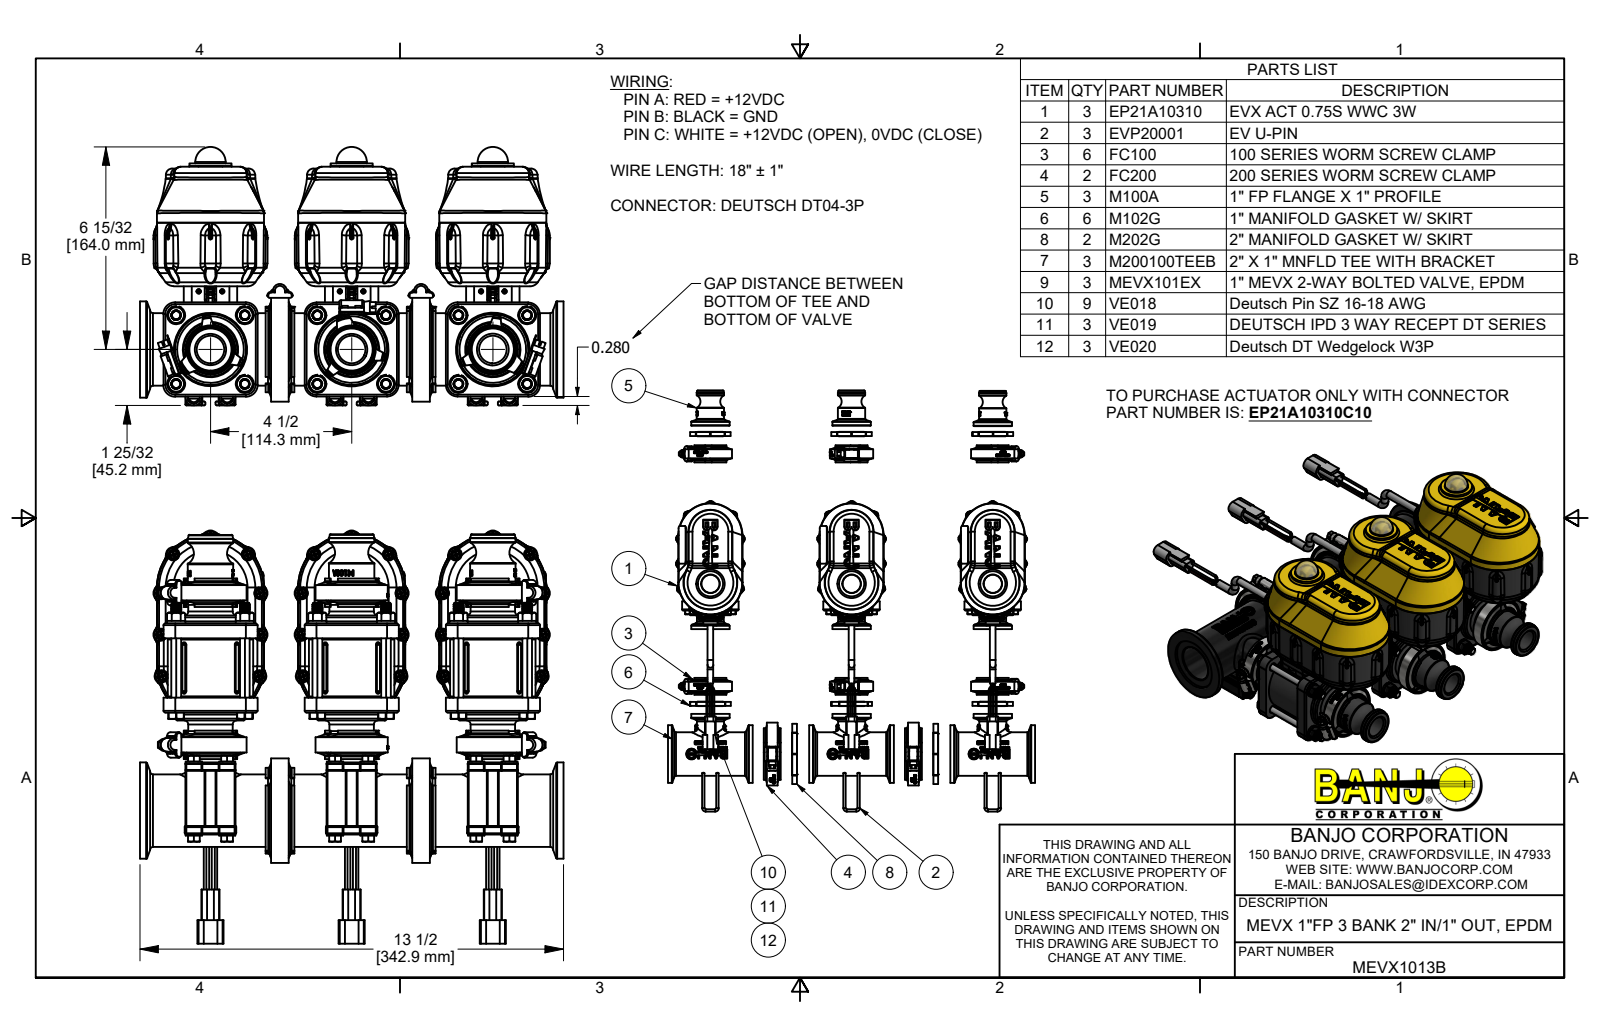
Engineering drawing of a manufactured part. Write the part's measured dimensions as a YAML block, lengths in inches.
part_name: "MEVX1013B; EP21A10310; EP10310; IRF4905 (+8 more)"
step_written_by: "Autodesk Inventor 2021 (AUTOMOTIVE_DESIGN)"
units: inches
bodies: {solids: 340, faces: 42176, planar: 11824, cylindrical: 12081, other: 18271}
overall_size: [13.5, 13.165, 8.247]
volume: 213.8
surface_area: 2465
round_holes:
  - {diameter: 0.095, count: 33}
  - {diameter: 0.15, count: 33}
  - {diameter: 0.08, count: 21}
  - {diameter: 0.25, count: 17}
  - {diameter: 0.125, count: 14}
  - {diameter: 0.107, count: 12}
  - {diameter: 0.126, count: 12}
  - {diameter: 0.136, count: 12}
  - {diameter: 0.148, count: 12}
  - {diameter: 0.15, count: 12}
  - {diameter: 0.17, count: 12}
  - {diameter: 0.252, count: 12}
round_bosses_or_shafts:
  - {diameter: 0.268, count: 180}
  - {diameter: 0.25, count: 51}
  - {diameter: 0.08, count: 45}
  - {diameter: 0.14, count: 33}
  - {diameter: 0.108, count: 33}
  - {diameter: 0.085, count: 33}
  - {diameter: 0.058, count: 18}
  - {diameter: 0.313, count: 15}
partial_cylinders:
  - {radius: 0.013, count: 540}
  - {radius: 0.04, count: 435}
  - {radius: 0.03, count: 359}
  - {radius: 0.02, count: 273}
  - {radius: 0.01, count: 264}
  - {radius: 0.005, count: 143}
  - {radius: 0.06, count: 126}
  - {radius: 0.125, count: 97}
face_to_face_distances: [4.5, 0.1, 2.565, 0.48, 9, 0.06, 0.211, 0.151, 2.365, 0.125]
hole_center_spacings: [4.5, 9, 2.69, 1.662, 1.891, 2.656, 2.715, 4.509]
